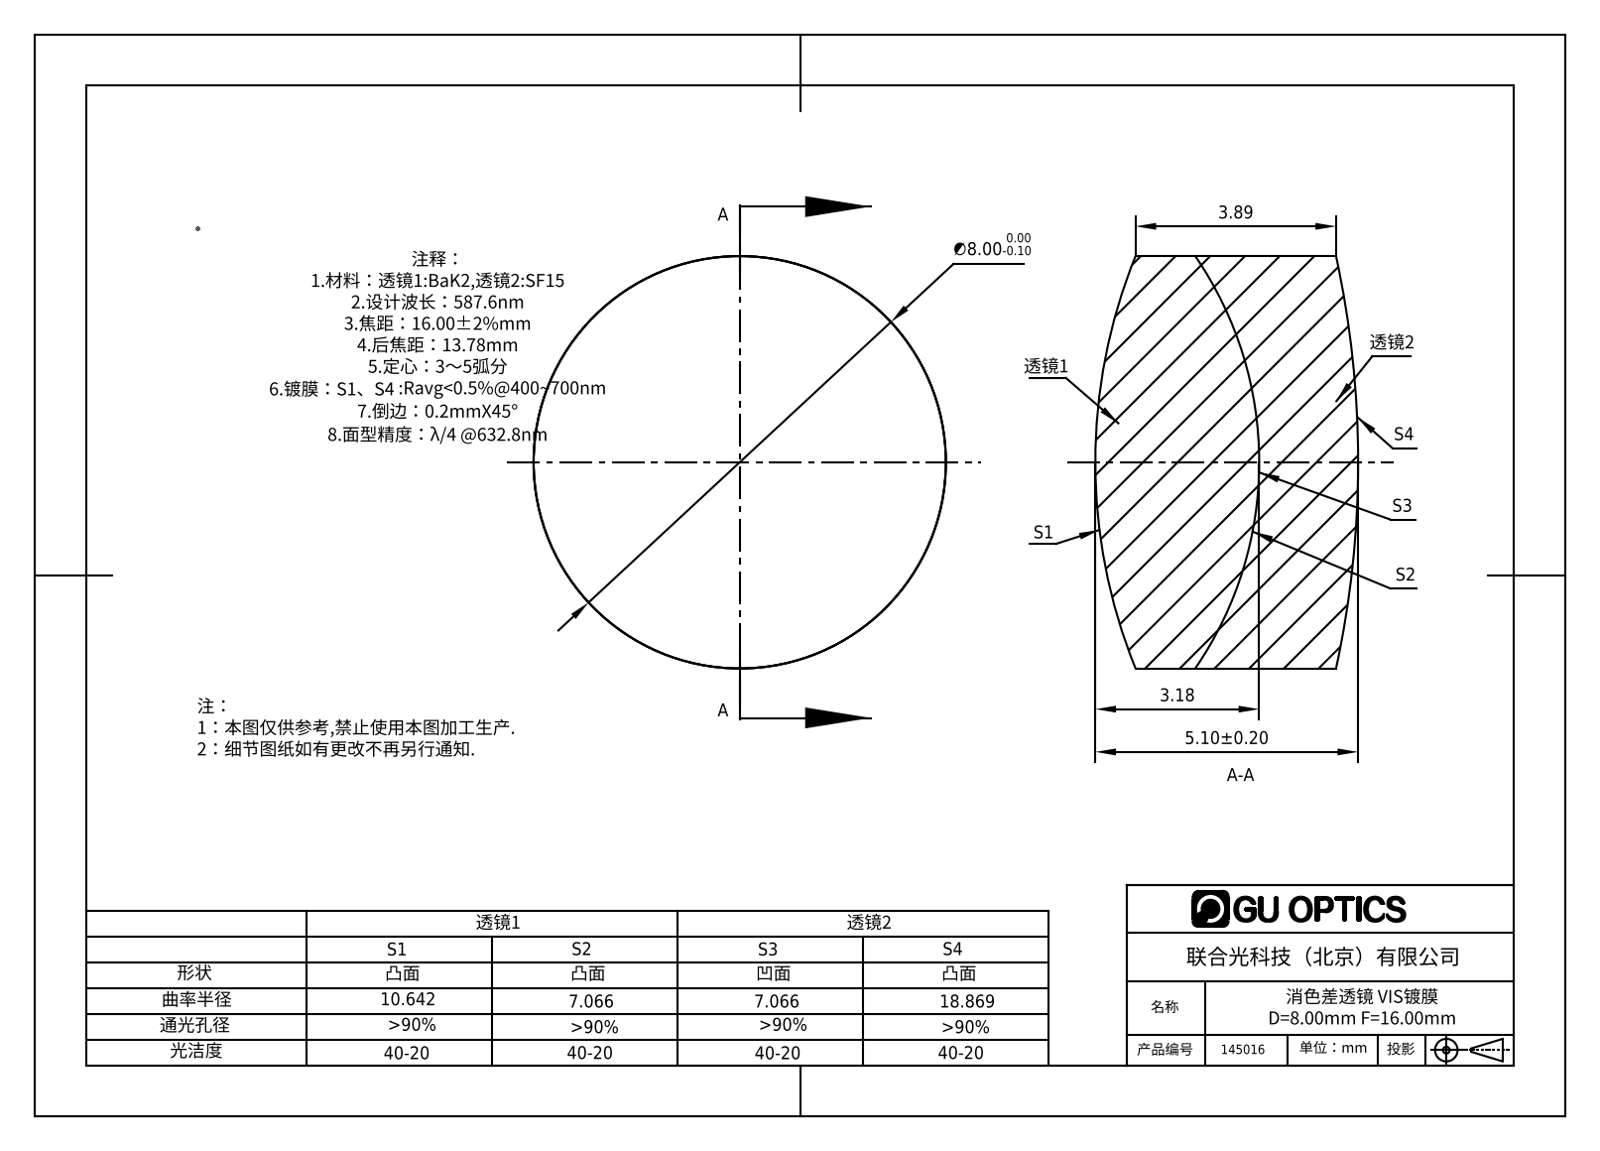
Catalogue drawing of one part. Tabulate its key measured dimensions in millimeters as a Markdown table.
| quantity | value |
| --- | --- |
| part name | 145016 |
| STEP written by | SolidWorks 2016 (AUTOMOTIVE_DESIGN) |
| units | millimeters |
| bodies | 2 solids, 12 faces (0 planar, 4 cylindrical, 8 other) |
| overall size | 8 × 8 × 5.1 |
| volume | 226 mm³ |
| surface area | 311 mm² |
| round bosses / shafts (diameter × count) | 8 × 1 |
